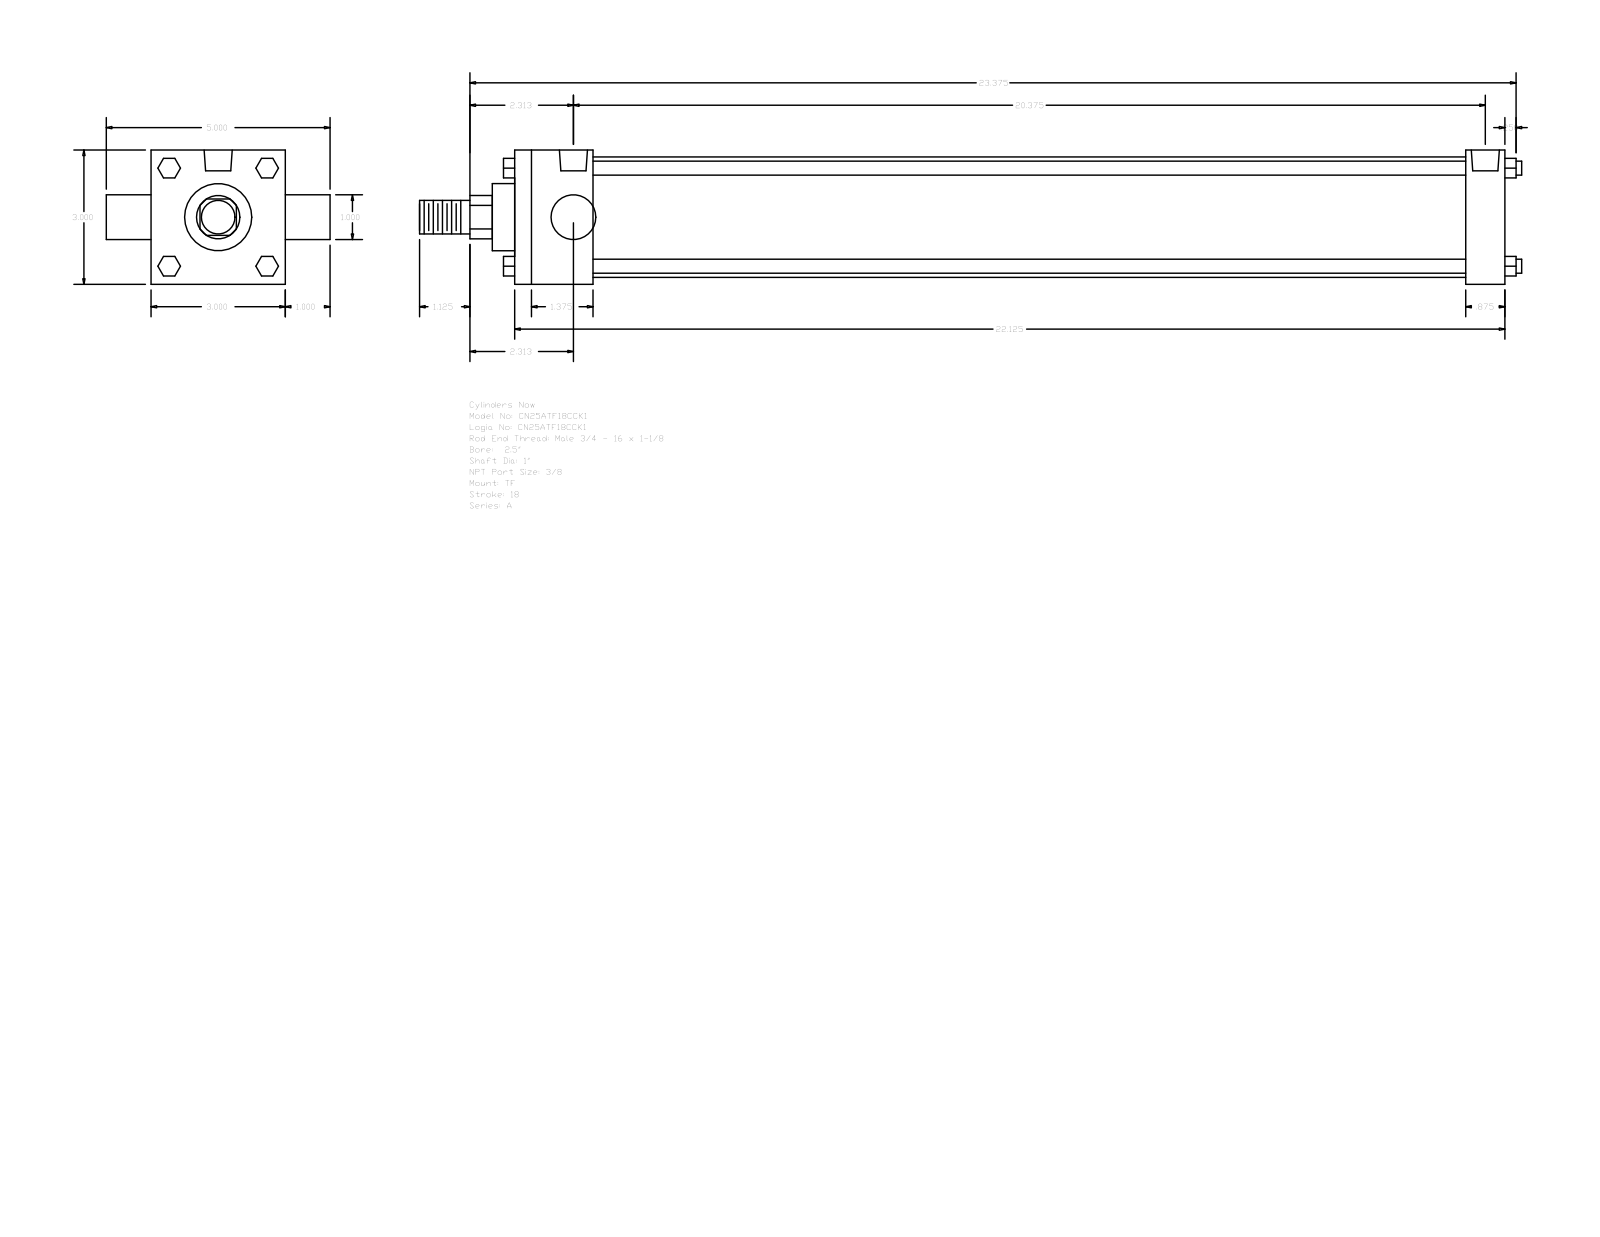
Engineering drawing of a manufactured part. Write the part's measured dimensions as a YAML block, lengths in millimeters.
part_name: "A_TF__0250_1"
step_written_by: "GSSL Pune (CONFIG_CONTROL_DESIGN)"
units: millimeters
bodies: {solids: 0, faces: 120, planar: 92, cylindrical: 28, other: 0}
overall_size: [625.48, 127, 76.2]
round_holes:
  - {diameter: 5.56, count: 3}
  - {diameter: 15.93, count: 2}
round_bosses_or_shafts:
  - {diameter: 7.94, count: 4}
  - {diameter: 25.4, count: 2}
  - {diameter: 68.33, count: 1}
  - {diameter: 38.1, count: 1}
  - {diameter: 19.05, count: 1}
partial_cylinders:
  - {radius: 12.29, count: 1}
face_to_face_distances: [76.2, 561.98, 44.45, 539.75, 495.3, 517.53, 22.23, 25.4, 101.6, 574.68]
hole_center_spacings: [2.38, 519.9, 517.52, 522.28]
